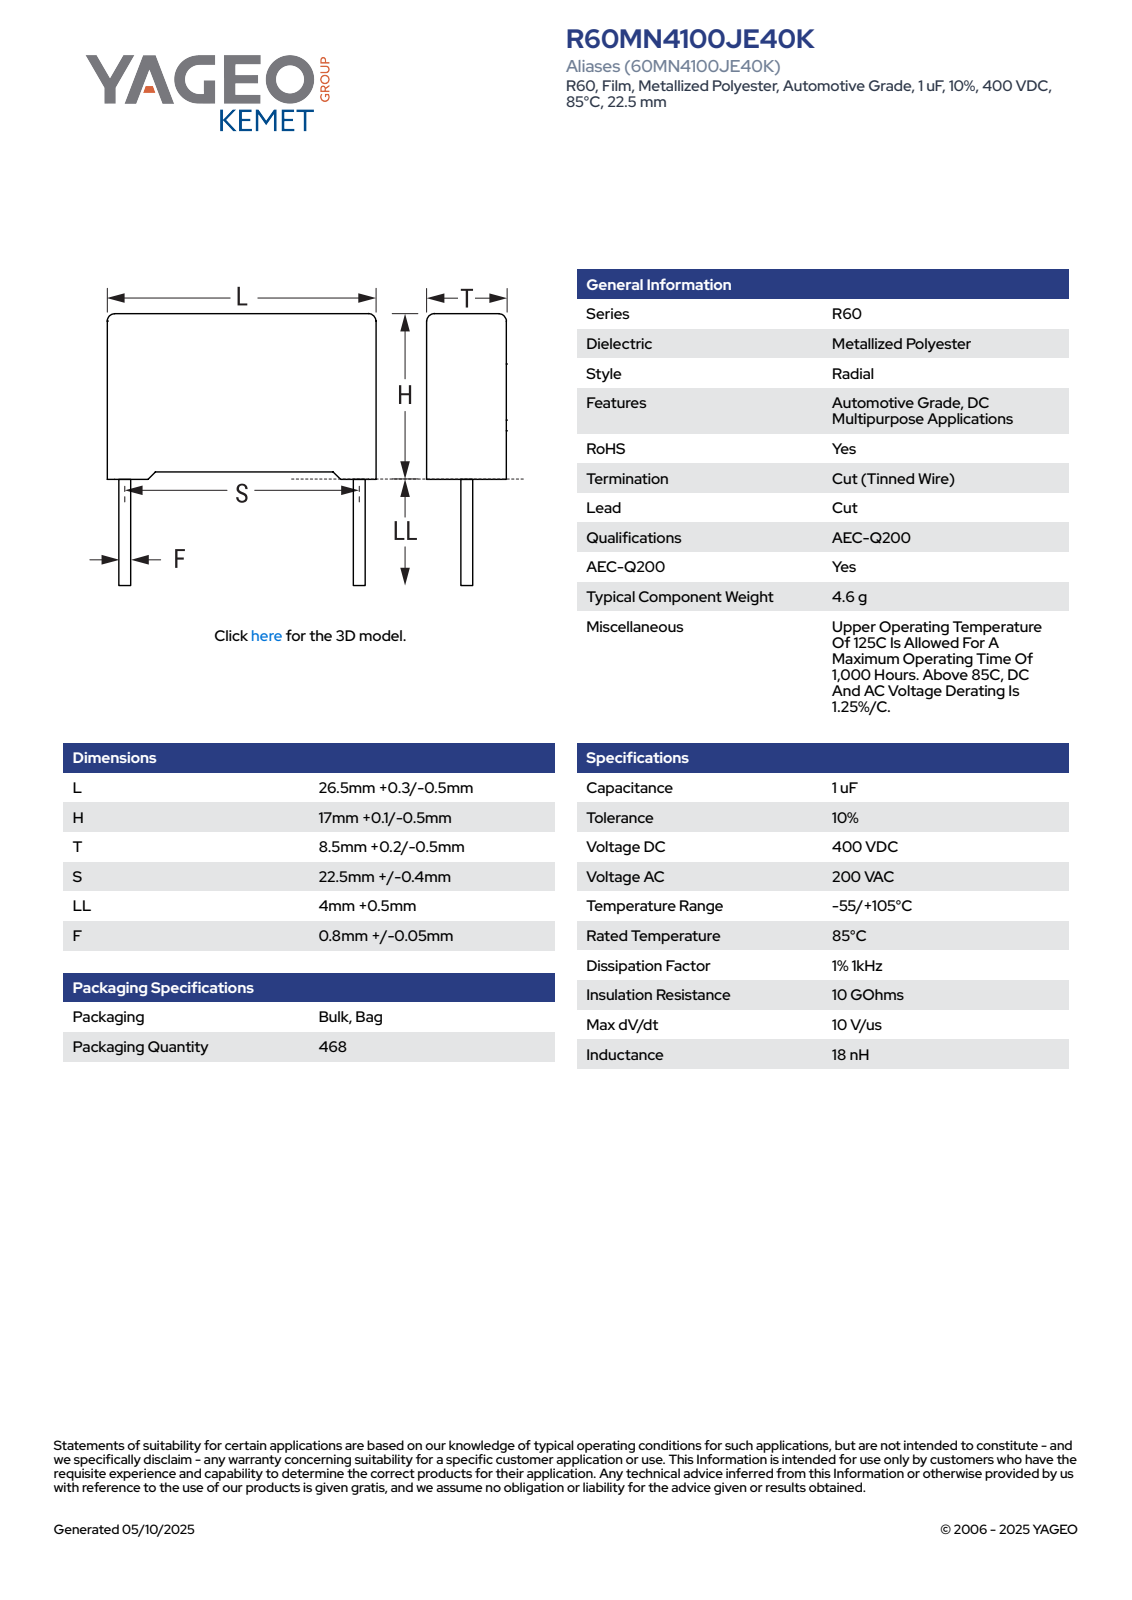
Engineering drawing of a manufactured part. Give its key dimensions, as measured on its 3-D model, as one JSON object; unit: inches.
{"part_name": "CFR_RB2_26.5X17X8.5_L26.8H17.1T8.7S22.5LL4.5F0.85", "step_written_by": "SolidWorks 2021 (AUTOMOTIVE_DESIGN)", "units": "inches", "bodies": {"solids": 4, "faces": 85, "planar": 77, "cylindrical": 8, "other": 0}, "overall_size": [1.055, 0.85, 0.343], "volume_in3": 0.234, "surface_area_in2": 2.714, "round_bosses_or_shafts": [[0.033, 2]], "partial_cylinders_radius": [[0.02, 4]], "face_to_face_distances": [0.343, 0.644, 1.055, 0.65, 0.035, 0.03, 0.023, 0.673, 0.307, 0.343]}
